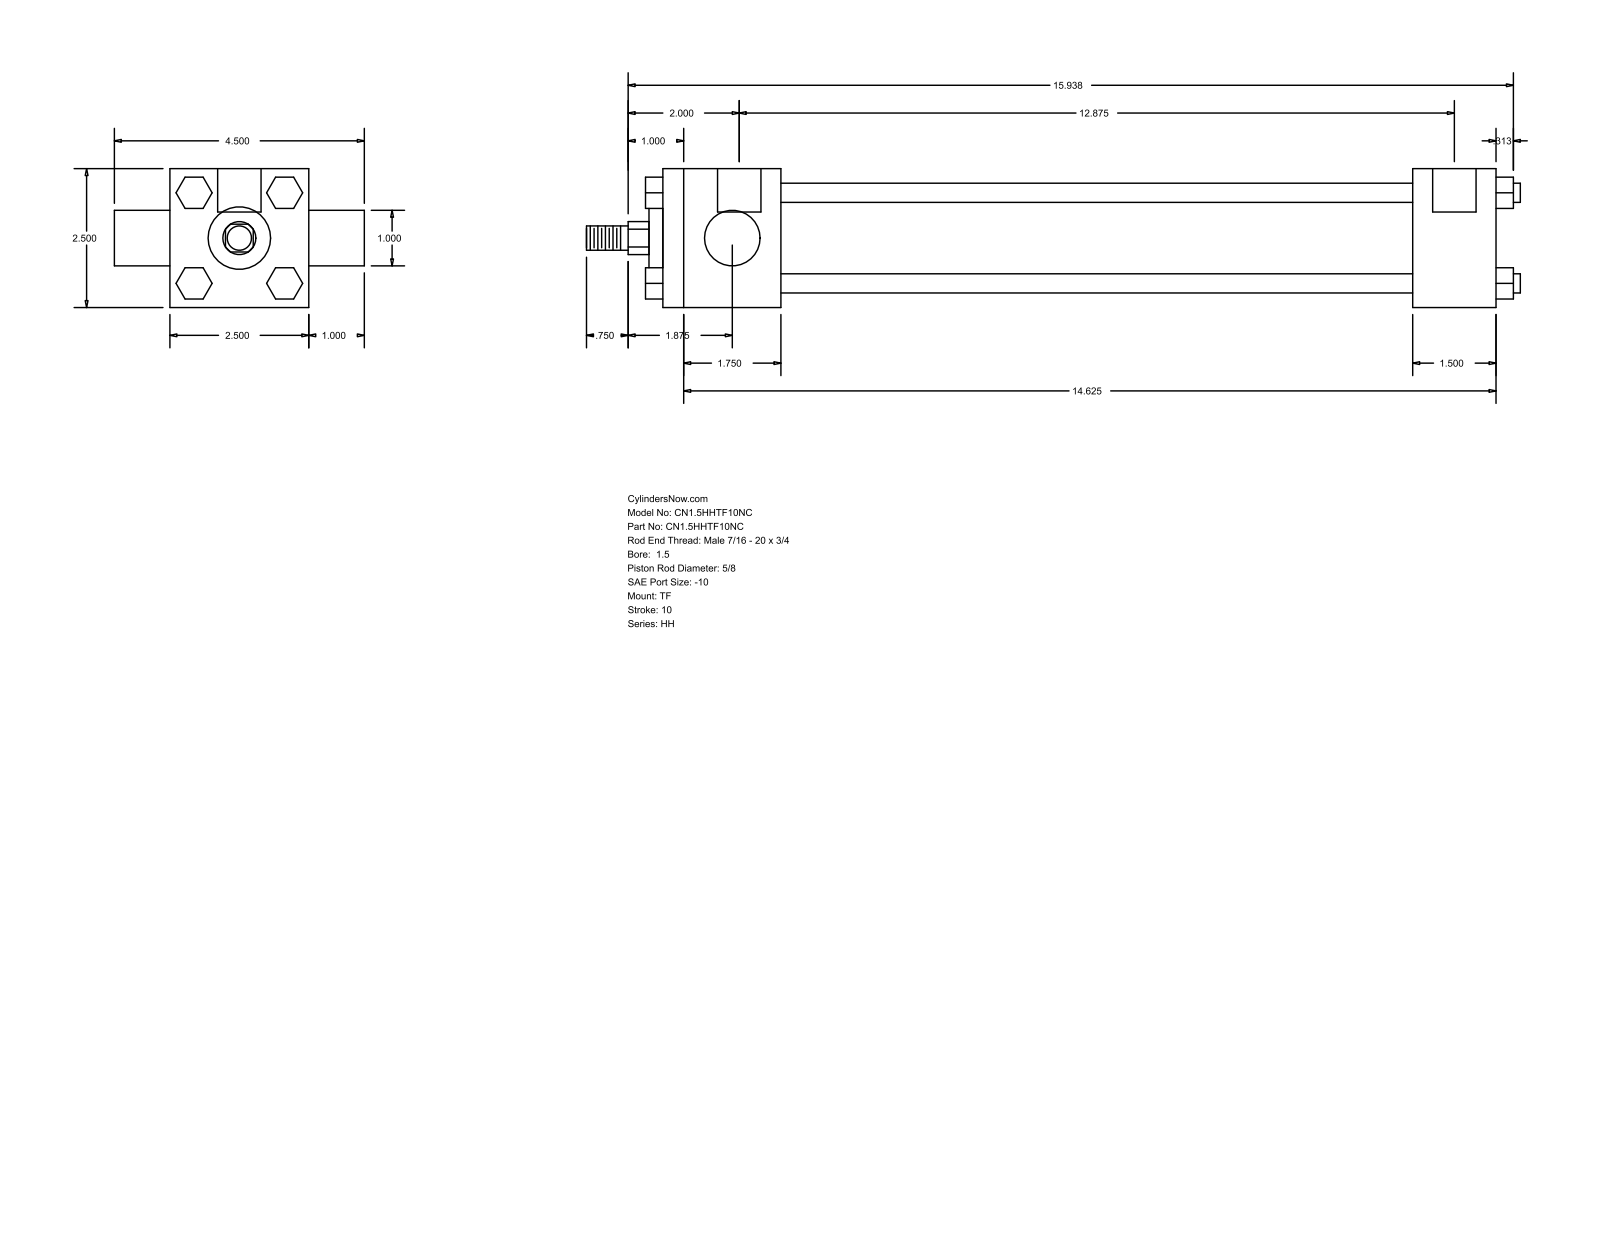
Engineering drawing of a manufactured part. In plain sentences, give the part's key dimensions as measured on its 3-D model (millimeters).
The part is named "HH_TF__0150_0.625". Its 3-D file was written by "GSSL Pune (CONFIG_CONTROL_DESIGN)". It is 0 solids with 120 faces: 92 planar, 28 cylindrical and 0 other. Overall it measures 427.04 by 114.3 by 63.5 millimeters. Round holes: 3 of diameter 5.56, 2 of diameter 19.84. Round bosses or shafts: 4 of diameter 8.76, 1 of diameter 44.45, 1 of diameter 28.57, 1 of diameter 25.4, 1 of diameter 15.88, 1 of diameter 11.11. Partial cylindrical surfaces (rounded edges, fillets, slot ends): 1 of radius 7.54. The main face-to-face distances are 63.5, 381, 53.97, 327.03, 342.89, 288.92, 38.11, 25.4, 88.9, 20.7. The hole center spacings are 1.59, 328.61, 327.02, 330.2.
